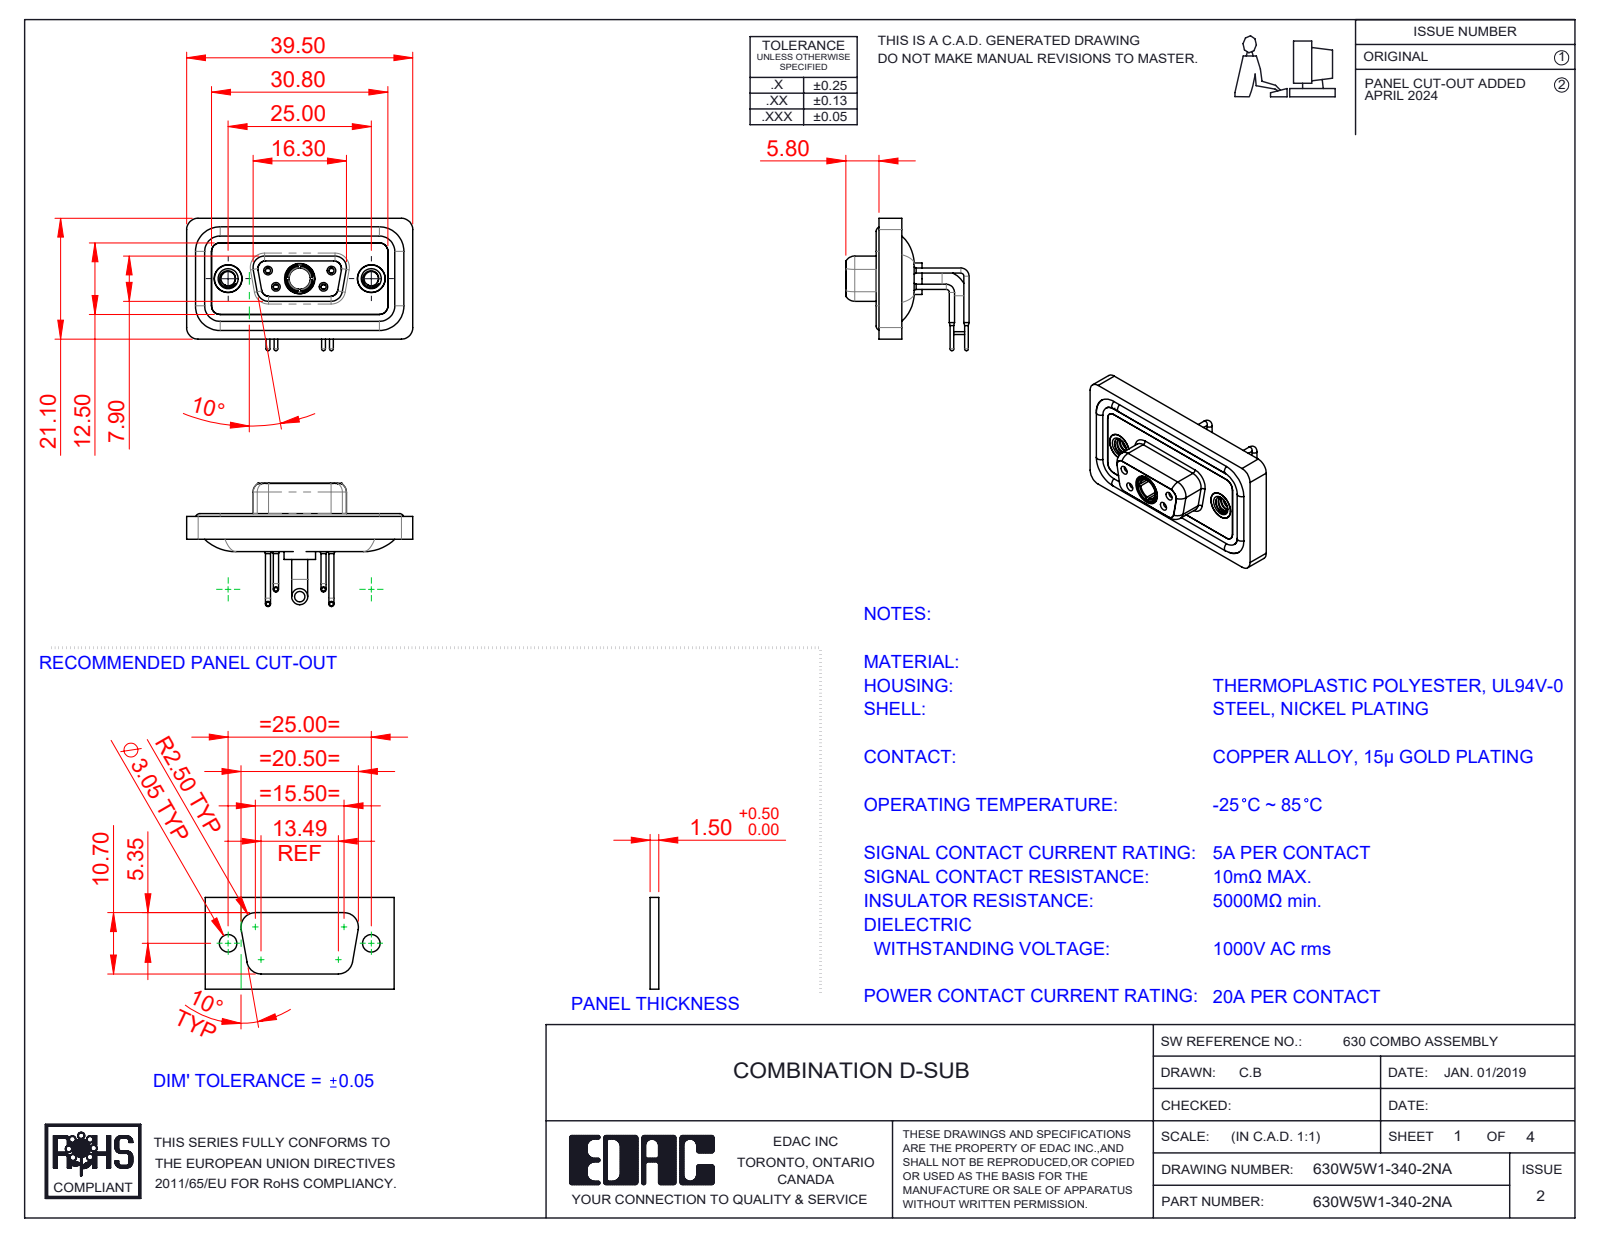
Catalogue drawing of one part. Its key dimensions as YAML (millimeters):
part_name: "630Combo Waterproof Housing_09 Contacts; 630Combo Shell Rear_09 Contacts; 630Combo Threaded Rivet_A; 630Combo Contact Row 1_50 Contacts (+5 more)"
step_written_by: "SolidWorks 2023 (CONFIG_CONTROL_DESIGN)"
units: millimeters
bodies: {solids: 13, faces: 670, planar: 194, cylindrical: 303, other: 173}
overall_size: [39.5, 23.12, 21.53]
volume: 4821
surface_area: 7846
round_holes:
  - {diameter: 0.9, count: 4}
  - {diameter: 1.1, count: 4}
  - {diameter: 1.5, count: 4}
  - {diameter: 2, count: 4}
  - {diameter: 4.85, count: 3}
  - {diameter: 1.6, count: 2}
  - {diameter: 1.7, count: 2}
  - {diameter: 2.5, count: 2}
  - {diameter: 4, count: 2}
  - {diameter: 4.05, count: 2}
  - {diameter: 5, count: 2}
  - {diameter: 3.7, count: 1}
round_bosses_or_shafts:
  - {diameter: 1.6, count: 6}
  - {diameter: 0.9, count: 4}
  - {diameter: 0.65, count: 4}
  - {diameter: 4.95, count: 2}
  - {diameter: 4.8, count: 2}
  - {diameter: 2.8, count: 2}
  - {diameter: 5.5, count: 1}
  - {diameter: 5.2, count: 1}
partial_cylinders:
  - {radius: 1.5, count: 18}
  - {radius: 2, count: 18}
  - {radius: 1.35, count: 8}
  - {radius: 1.6, count: 8}
  - {radius: 0.25, count: 4}
  - {radius: 0.5, count: 4}
  - {radius: 0.6, count: 4}
  - {radius: 0.65, count: 4}
face_to_face_distances: [0.4, 1.8, 1.1, 2.9, 2.5, 1.6, 3.1, 2.1, 1.5, 0.5]
hole_center_spacings: [3.16, 5.72, 7.1, 12.5, 18.1, 4.39, 4.4, 8.31]
